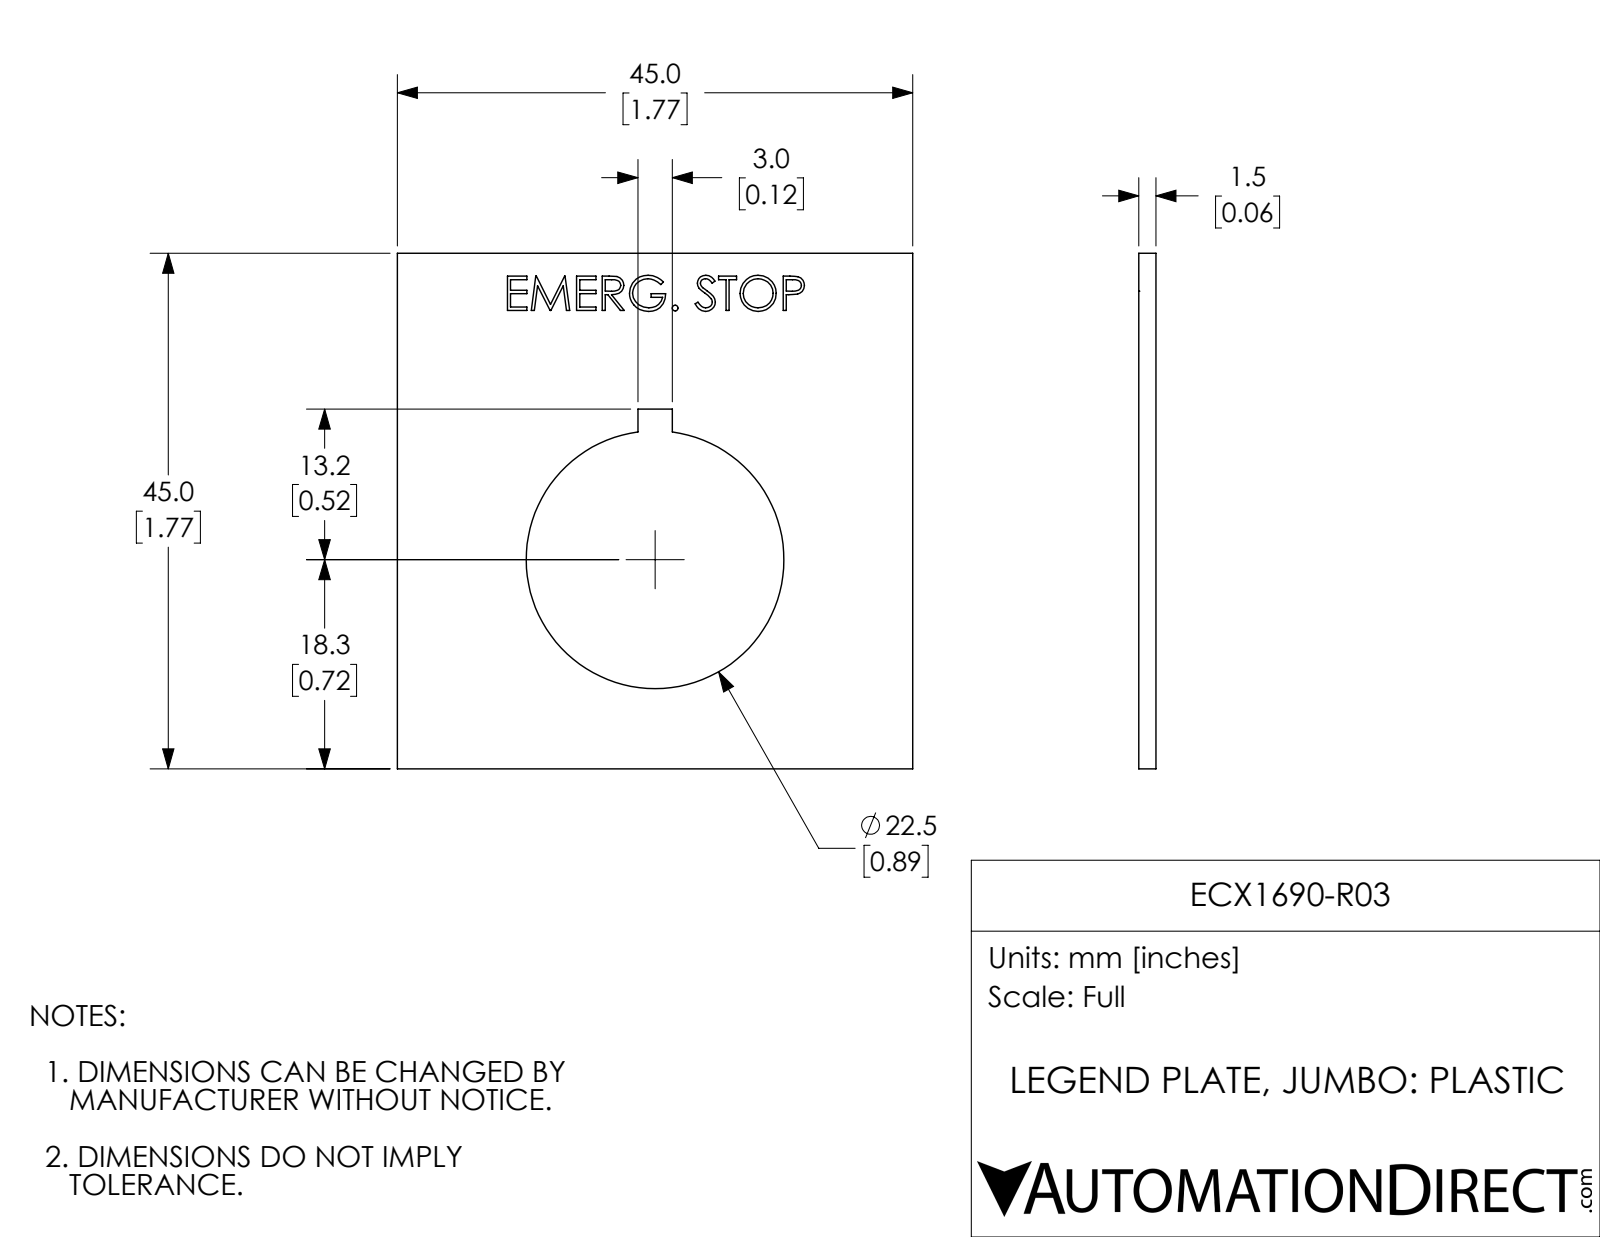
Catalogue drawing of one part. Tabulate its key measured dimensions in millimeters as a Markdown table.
| quantity | value |
| --- | --- |
| part name | ECX1690-R03 |
| STEP written by | SolidWorks 2018 (AUTOMOTIVE_DESIGN) |
| units | millimeters |
| bodies | 1 solid, 142 faces (92 planar, 3 cylindrical, 47 other) |
| overall size | 45 × 45 × 1.5 |
| volume | 2 430 mm³ |
| surface area | 3 629 mm² |
| round holes (diameter × count) | 22.5 × 1 |
| main face-to-face distances | 1.5, 45, 1.5, 21, 24, 31.4, 13.6, 3, 5, 1.4 |
